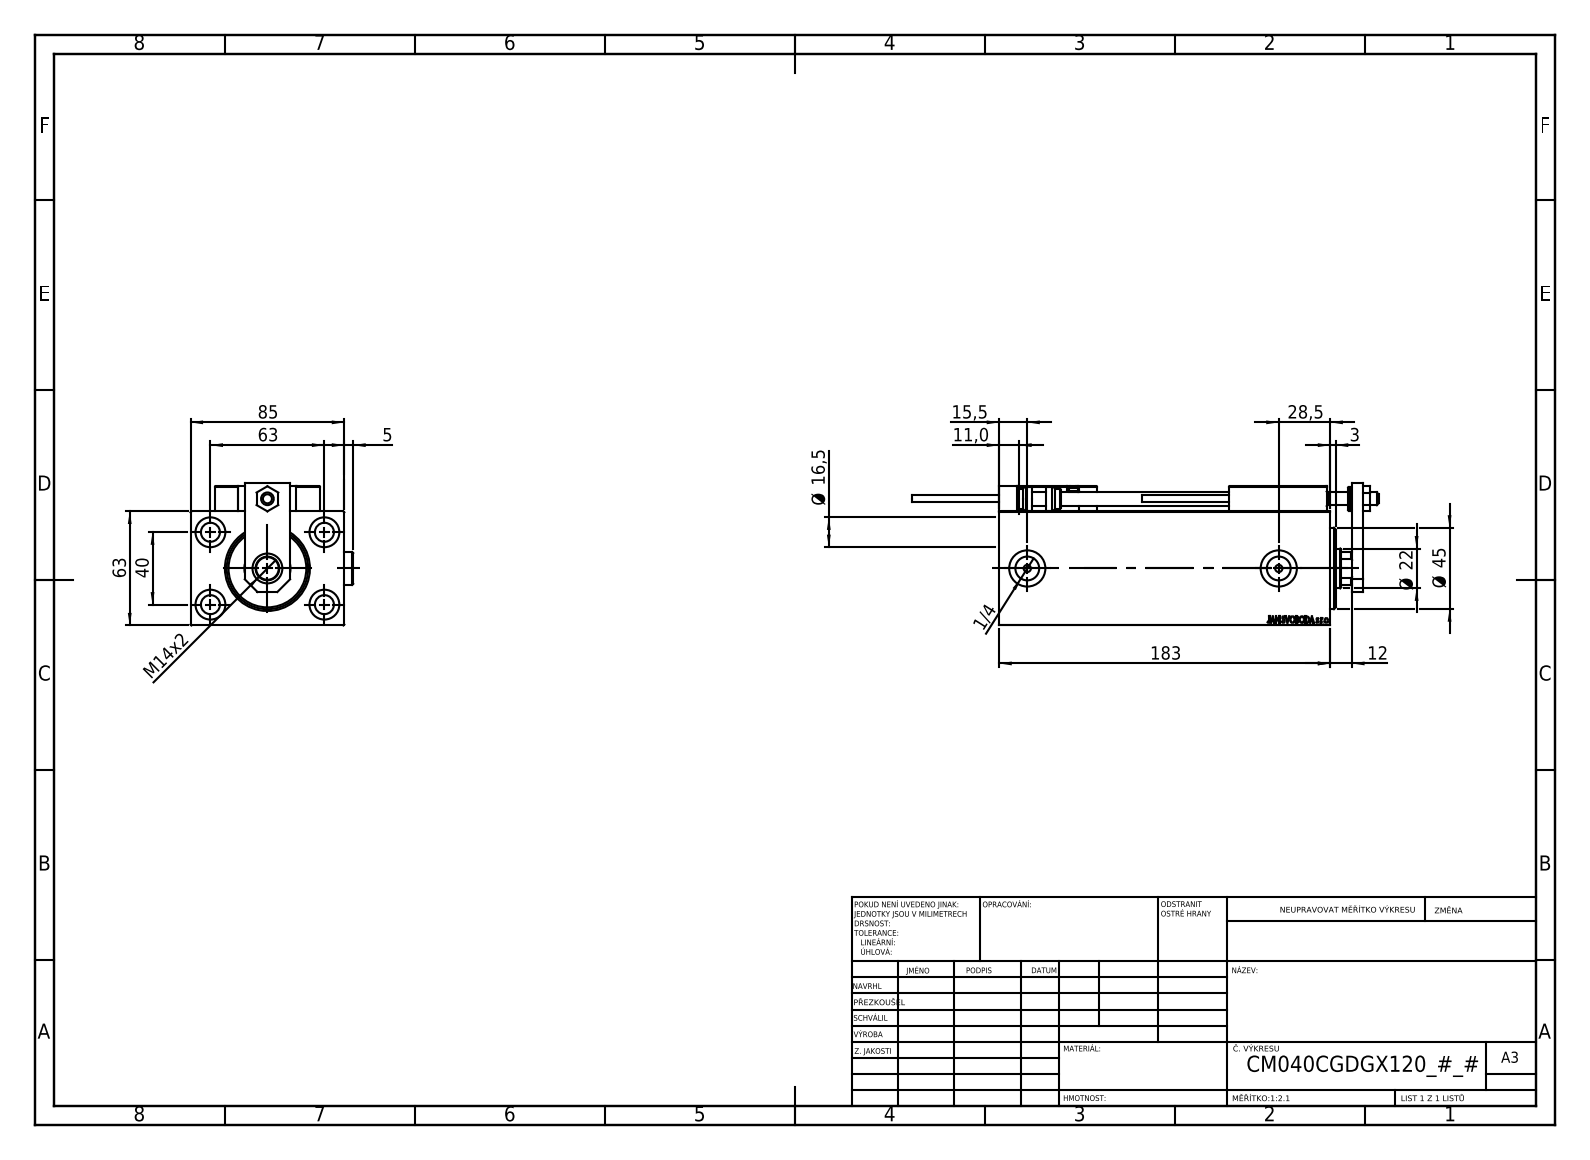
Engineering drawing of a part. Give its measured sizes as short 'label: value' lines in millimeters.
name: NUT_D12; V450CM_C_VCP; SWITCH X; ALLEN BOLT D5 (+7 more)
written by: SolidWorks 2019 (CONFIG_CONTROL_DESIGN)
unit: mm
bodies: 25 solids, 1336 faces (594 planar, 204 cylindrical, 538 other)
size: 257.7 × 89.9 × 78.5
volume: 853 116 mm³; area: 166 231 mm²
holes: 6× ⌀4, 5× ⌀8, 5× ⌀16.5, 4× ⌀3.2, 4× ⌀10.5, 2× ⌀5, 2× ⌀13.16, 2× ⌀20, 1× ⌀7, 1× ⌀12.5, 1× ⌀22, 1× ⌀25.5
bosses: 2× ⌀18, 2× ⌀5, 2× ⌀3.8, 1× ⌀13, 1× ⌀11
rounds: 30× R0.3, 2× R3, 1× R10.5
face distances: 63, 85, 12, 171, 183, 14, 77, 15, 18, 30
hole spacings: 37.31, 11.37, 20, 29.59, 29.69, 36.06, 36.53, 40
